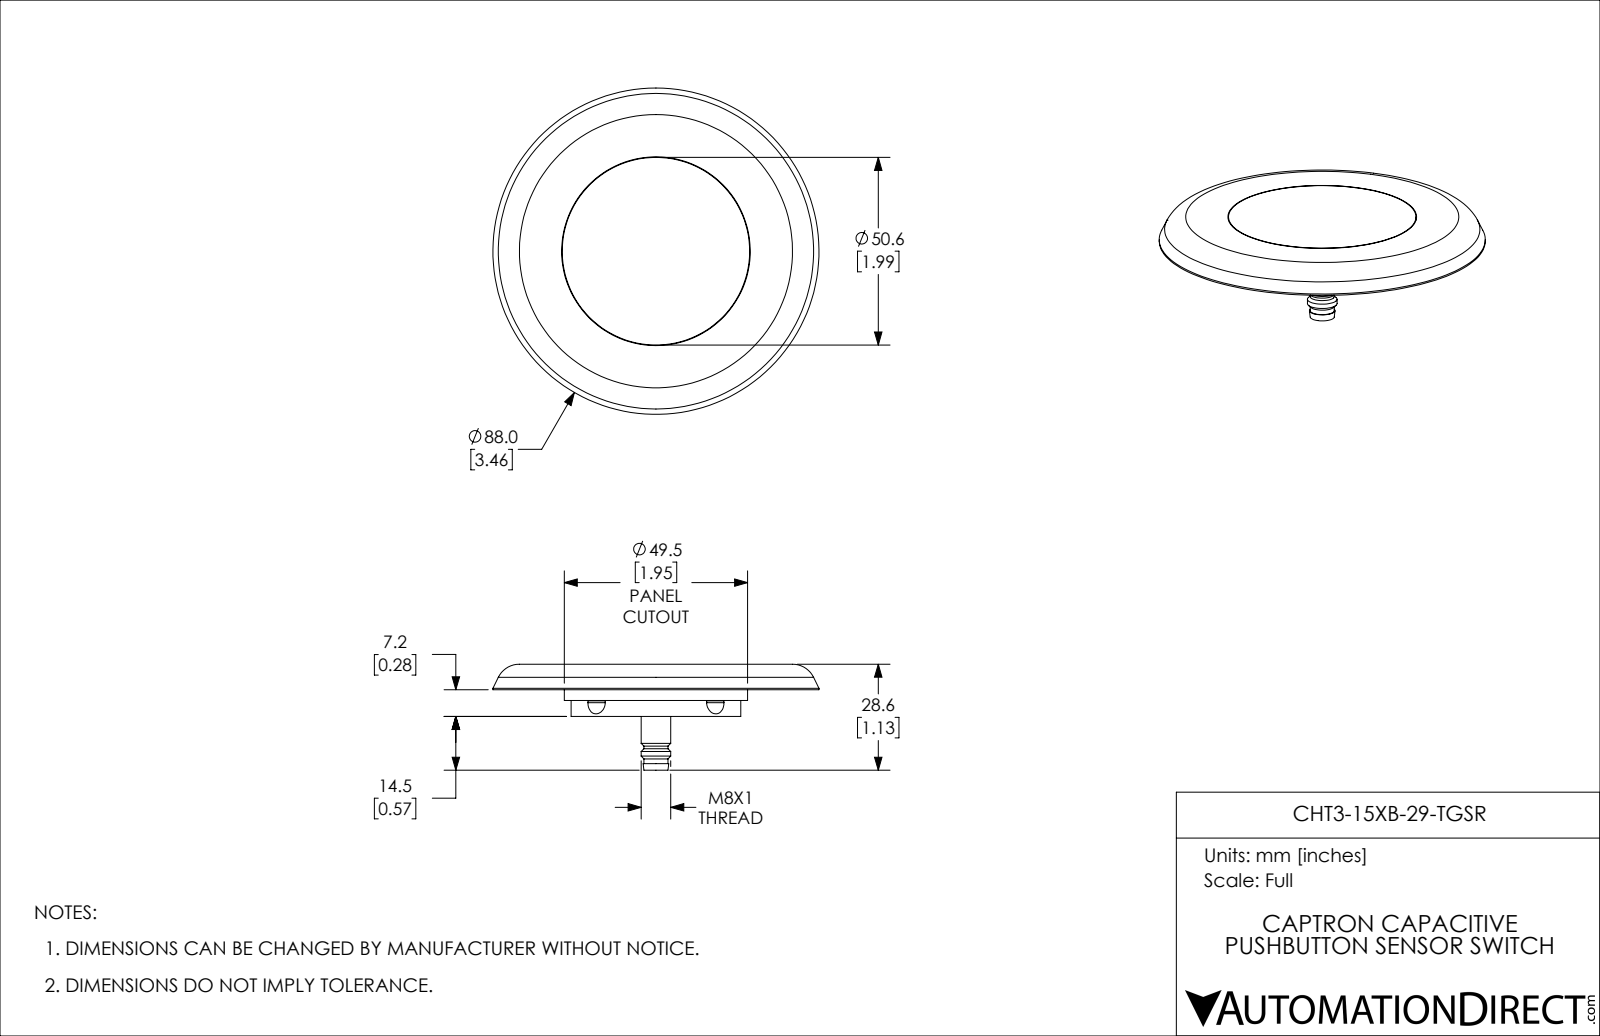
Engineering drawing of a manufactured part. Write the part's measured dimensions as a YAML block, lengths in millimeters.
part_name: "CHT3-15XB-29-TGSR"
step_written_by: "SolidWorks 2019 (CONFIG_CONTROL_DESIGN)"
units: millimeters
bodies: {solids: 10, faces: 90, planar: 25, cylindrical: 40, other: 25}
overall_size: [88, 88, 28.6]
volume: 49980
surface_area: 21720
round_holes:
  - {diameter: 46.1, count: 1}
  - {diameter: 50.9, count: 1}
round_bosses_or_shafts:
  - {diameter: 1, count: 5}
  - {diameter: 50.6, count: 1}
  - {diameter: 49.5, count: 1}
  - {diameter: 45.8, count: 1}
  - {diameter: 8, count: 1}
  - {diameter: 6.5, count: 1}
partial_cylinders:
  - {radius: 5, count: 4}
  - {radius: 0.5, count: 2}
  - {radius: 0.9, count: 1}
  - {radius: 1, count: 1}
  - {radius: 2.9, count: 1}
face_to_face_distances: [6.9, 4.6, 2.3, 7.2, 11.8, 14.1, 0.5, 4.3, 7.7, 2.9]
